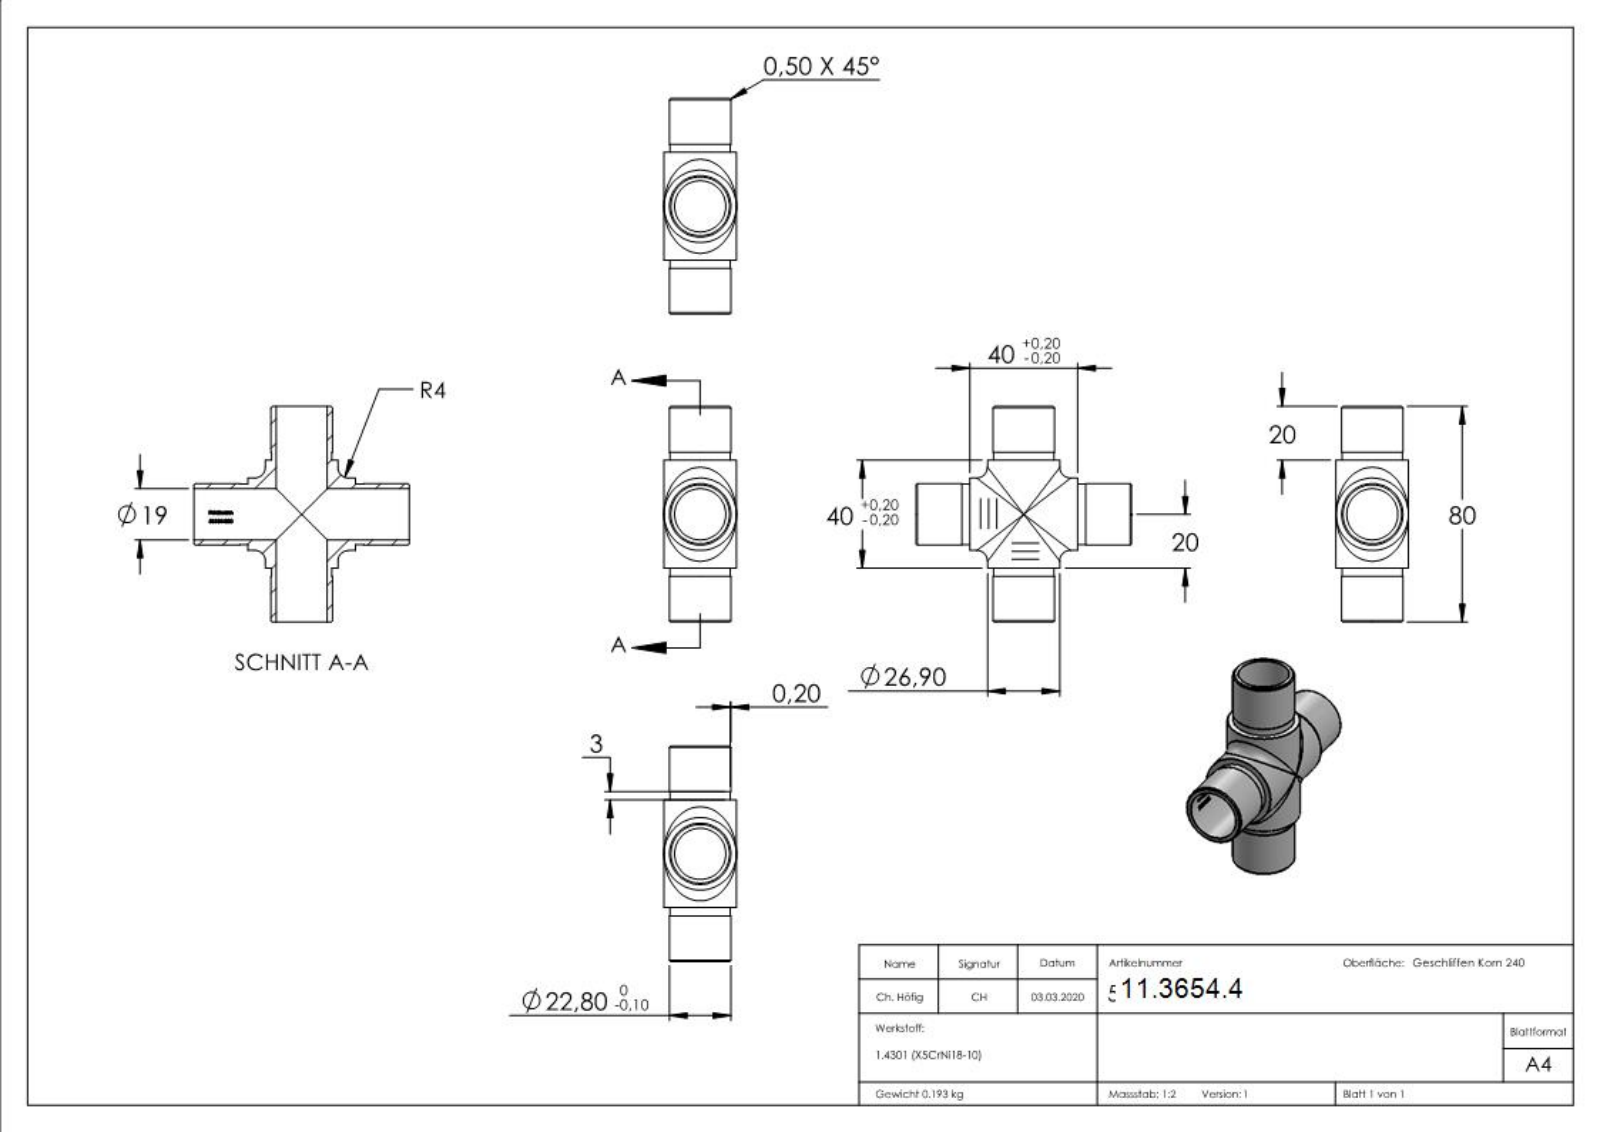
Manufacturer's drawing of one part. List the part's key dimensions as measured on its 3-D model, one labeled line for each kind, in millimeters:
Part name (STEP PRODUCT): 56184-320
STEP written by: SolidWorks 2015 (CONFIG_CONTROL_DESIGN)
Units: millimetres
Bodies: 1 solid, 267 faces (107 planar, 41 cylindrical, 119 other)
Overall size (bounding box): 80 × 80 × 26.9
Volume: 24 383 mm³ · Surface area: 18 769 mm²
Round holes (diameter × count): ⌀19 ×2
Round bosses / shafts (diameter × count): ⌀26.9 ×2, ⌀22.8 ×2, ⌀22.4 ×2
Partial cylindrical surfaces — rounded edges, fillets, slot ends (radius × count): R9.6 ×1
Main face-to-face distances: 20, 60, 40, 80, 17, 63, 3, 43, 46, 1.26
